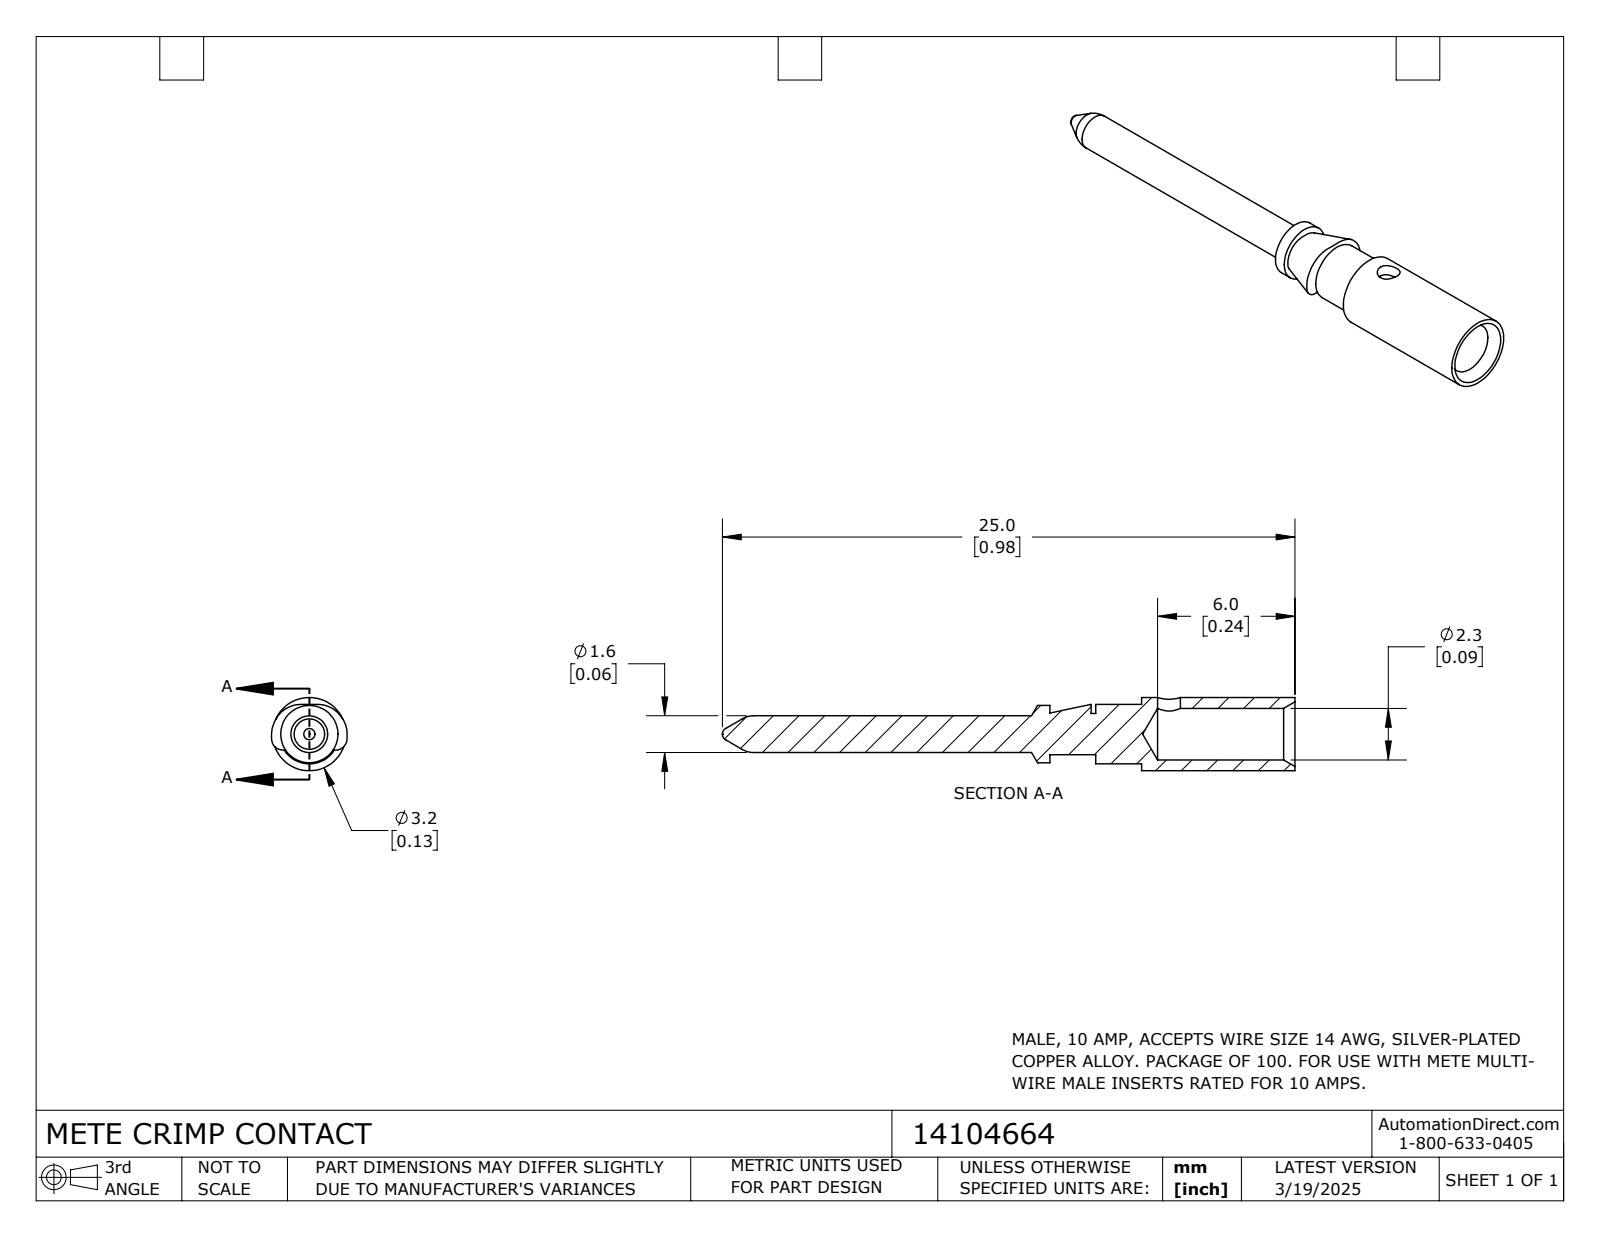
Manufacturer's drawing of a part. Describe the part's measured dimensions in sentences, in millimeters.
The part is named "14104664". Its 3-D file was written by "SolidWorks 2024 (CONFIG_CONTROL_DESIGN)". It is 1 solid with 33 faces: 6 planar, 14 cylindrical and 13 other. Overall it measures 25 by 3.3 by 3.2 millimeters. Its volume is 76 cubic millimeters and its surface area 233 square millimeters. Round holes: 1 of diameter 1, 1 of diameter 2.25. Round bosses or shafts: 1 of diameter 3.2, 1 of diameter 2.6, 1 of diameter 2.5, 1 of diameter 1.8, 1 of diameter 1.6. The main face-to-face distances are 2, 2.2, 4, 1.8, 6.7, 8.7, 8.9, 10.7, 25, 18.3.
